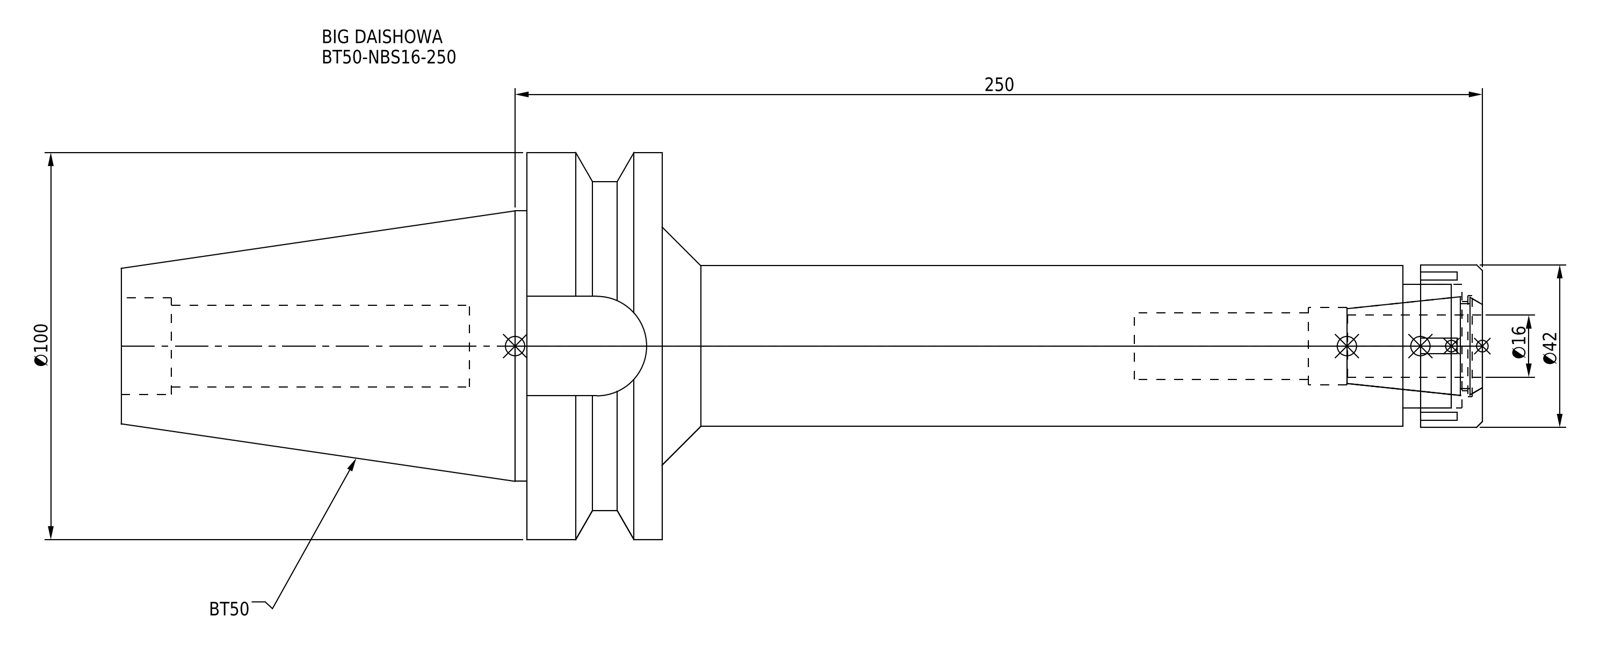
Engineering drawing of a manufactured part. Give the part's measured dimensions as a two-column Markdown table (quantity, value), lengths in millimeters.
| quantity | value |
| --- | --- |
| part name | BT50-NBS16-250.stp; BT50-NBS16-250; BT50-NBS16-250-FreeParts; DXF_TEMP_ASSY_ASM_4_ASM.stp (+3 more) |
| STEP written by | SolidWorks 2019 (CONFIG_CONTROL_DESIGN) |
| units | millimeters |
| bodies | 2 solids, 89 faces (45 planar, 30 cylindrical, 14 other) |
| overall size | 351.8 × 100 × 100 |
| volume | 723 404 mm³ |
| surface area | 87 619 mm² |
| round holes (diameter × count) | 17.3 × 1, 20 × 1, 21.2 × 1, 23 × 1, 25 × 1, 26 × 1, 32 × 1 |
| round bosses / shafts (diameter × count) | 100 × 1, 85 × 1, 69.85 × 1, 42 × 1, 41.5 × 1 |
| partial cylindrical surfaces (radius × count) | 12.85 × 1 |
| main face-to-face distances | 35, 212, 247, 351.8, 139.8, 104.8, 70.8, 8, 90, 261.8 |
